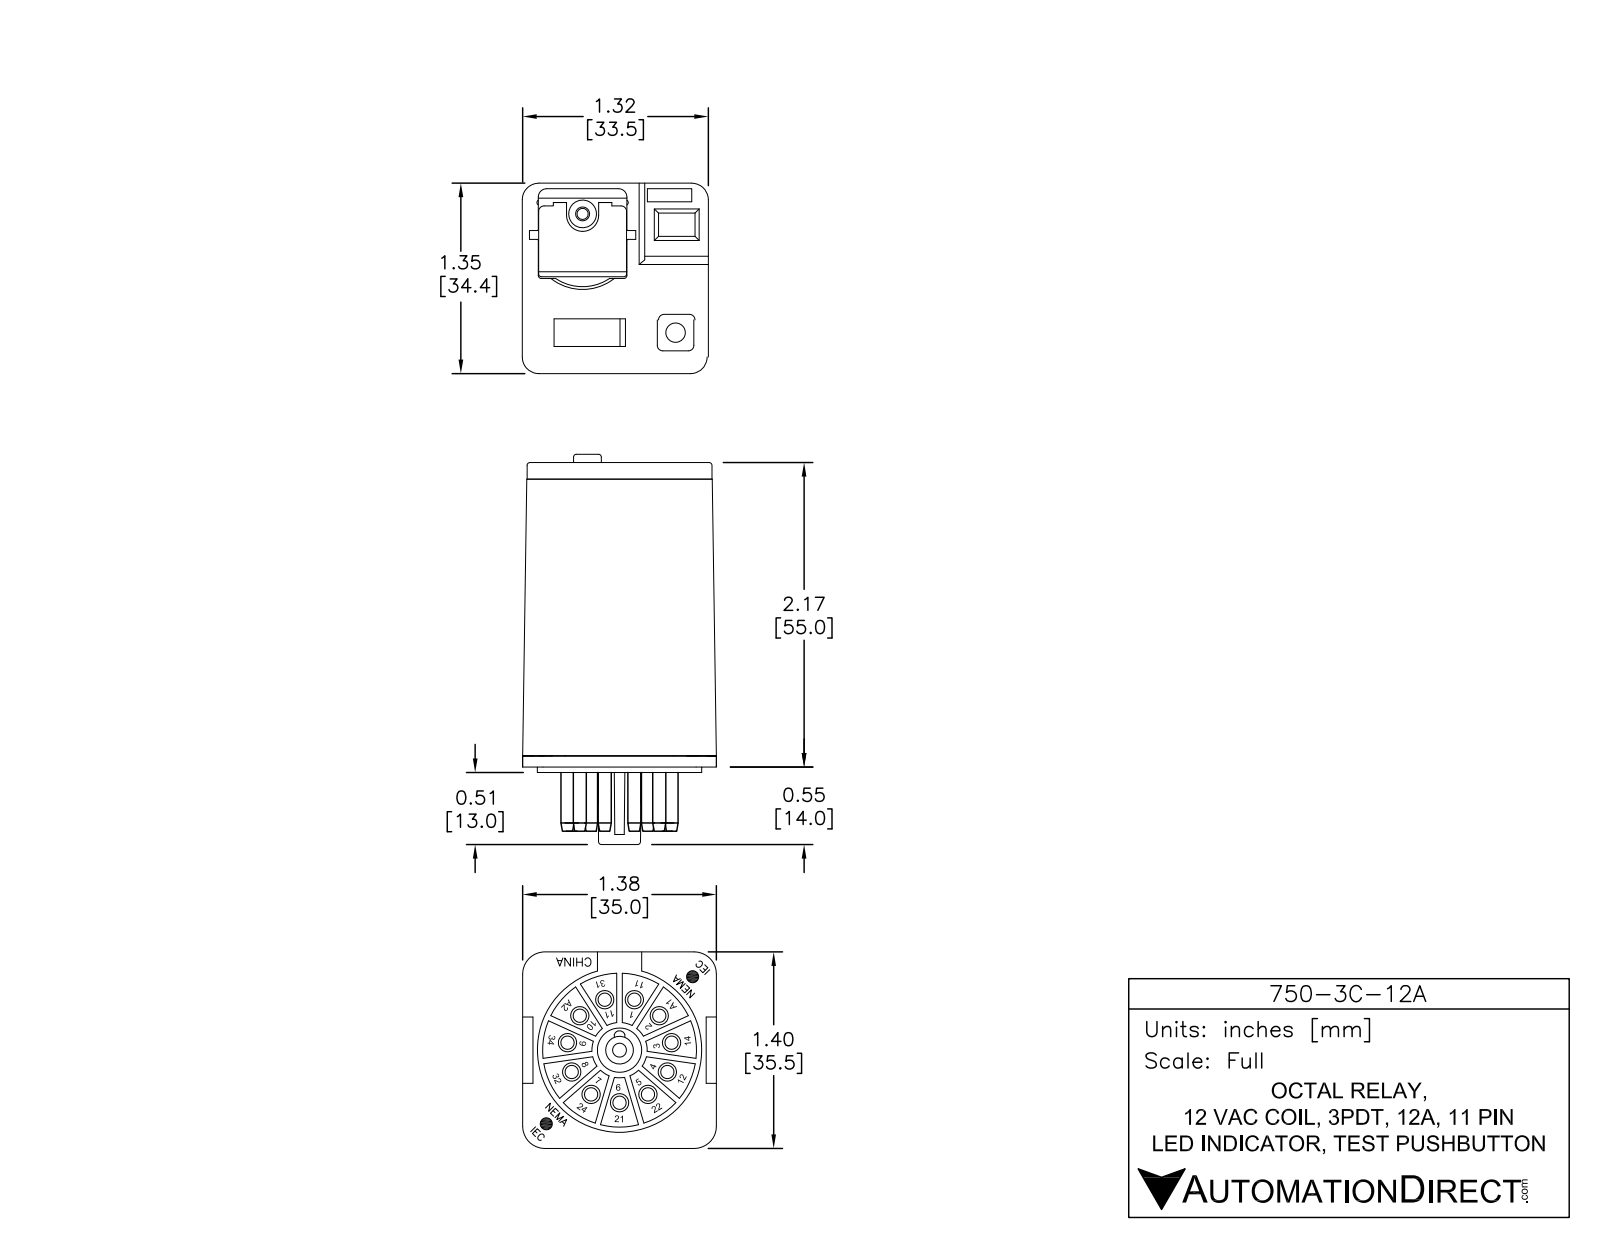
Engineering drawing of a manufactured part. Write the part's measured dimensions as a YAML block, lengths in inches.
part_name: "750-3C-12A"
step_written_by: "SolidWorks 2013 (AUTOMOTIVE_DESIGN)"
units: inches
bodies: {solids: 5, faces: 387, planar: 199, cylindrical: 104, other: 84}
overall_size: [2.74, 1.383, 1.378]
volume: 4.127
surface_area: 25.86
round_holes:
  - {diameter: 0.098, count: 1}
round_bosses_or_shafts:
  - {diameter: 0.118, count: 11}
  - {diameter: 0.087, count: 11}
  - {diameter: 1.161, count: 1}
  - {diameter: 0.315, count: 1}
  - {diameter: 0.189, count: 1}
  - {diameter: 0.033, count: 1}
partial_cylinders:
  - {radius: 0.02, count: 4}
  - {radius: 0.118, count: 4}
  - {radius: 0.01, count: 2}
  - {radius: 0.039, count: 2}
  - {radius: 0.03, count: 1}
  - {radius: 0.039, count: 1}
  - {radius: 0.098, count: 1}
  - {radius: 0.197, count: 1}
face_to_face_distances: [1.378, 1.969, 2.156, 0.118, 2.087, 0.069, 2.037, 0.039, 2.1, 0.055]
